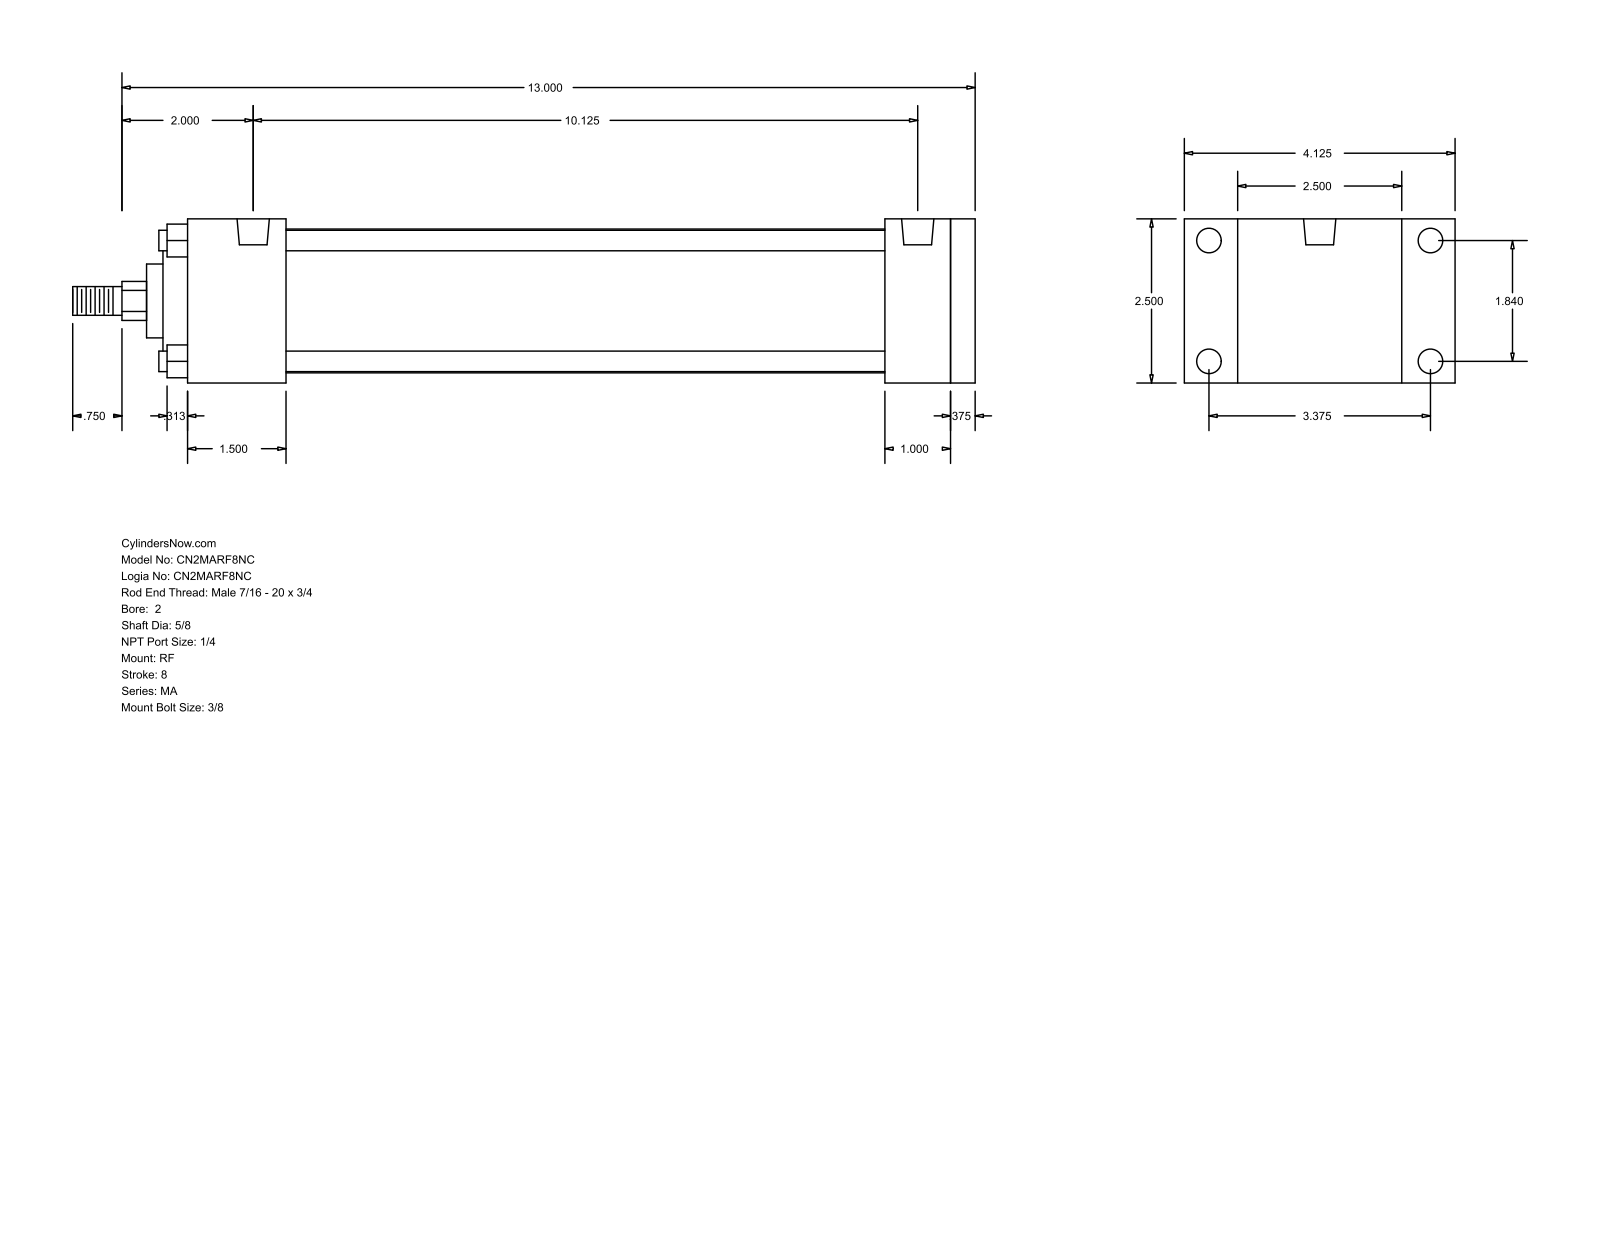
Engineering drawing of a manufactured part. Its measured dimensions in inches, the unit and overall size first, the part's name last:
Units: inches
Overall size (bounding box): 13.75 × 4.125 × 2.5
Round holes (diameter × count): ⌀0.313 ×4, ⌀0.375 ×4, ⌀0.492 ×2
Round bosses / shafts (diameter × count): ⌀0.313 ×4, ⌀2.19 ×1, ⌀2 ×1, ⌀1.125 ×1, ⌀0.625 ×1, ⌀0.437 ×1
Partial cylindrical surfaces — rounded edges, fillets, slot ends (radius × count): R0.297 ×1
Main face-to-face distances: 2.5, 0.375, 12, 1.5, 1.375, 12.375, 11.625, 10.125, 10.5, 10.625
Hole centre spacings: 1.84, 3.375, 3.844, 10.125
Bodies: 0 solids, 94 faces (65 planar, 29 cylindrical, 0 other)
Part name (STEP PRODUCT): MA_RF__0200_0.625
STEP written by: GSSL Pune (CONFIG_CONTROL_DESIGN)
